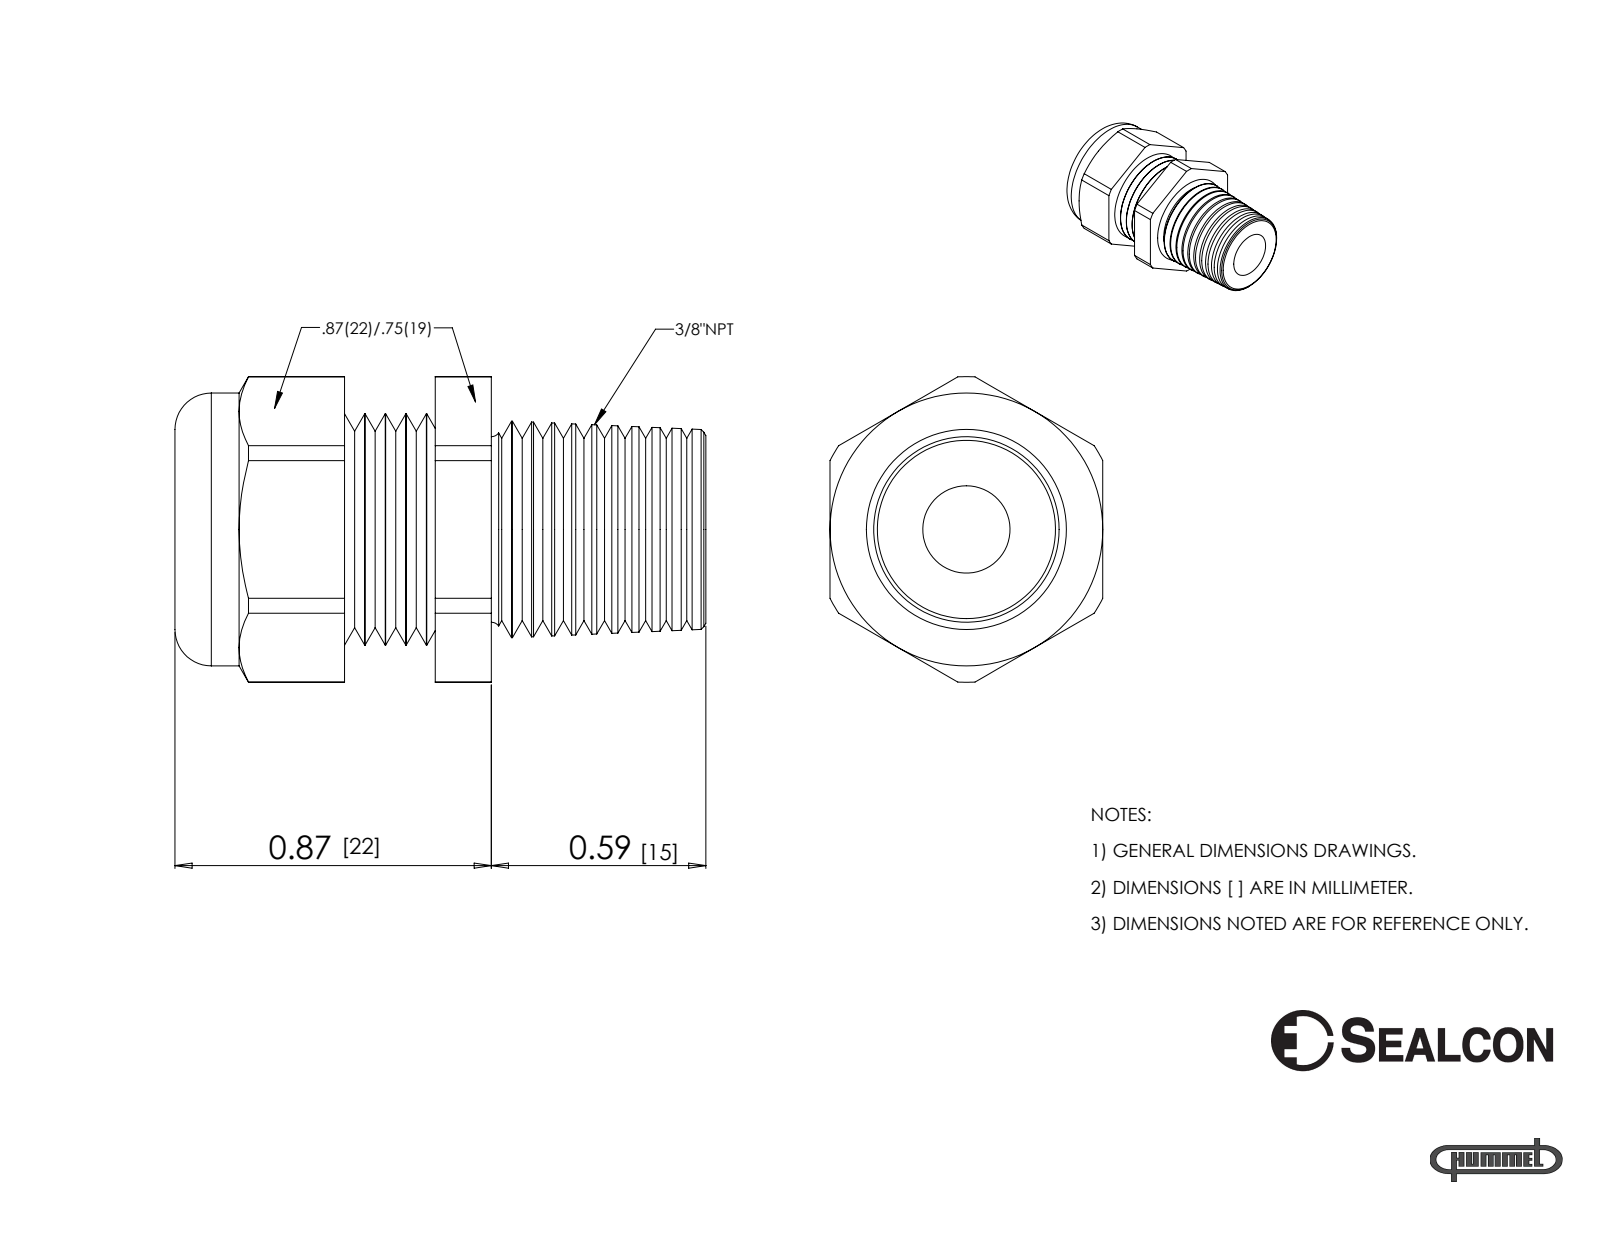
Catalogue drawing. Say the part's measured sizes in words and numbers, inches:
The part is named "CD09NR-GY". Its 3-D file was written by "SolidWorks 2009 (CONFIG_CONTROL_DESIGN)". It is 2 solids with 152 faces: 20 planar, 32 cylindrical and 100 other. Overall it measures 1.46 by 0.84 by 0.75 inches. Its volume is 0.407 cubic inches and its surface area 7.52 square inches. Round holes: 1 of diameter 0.24, 1 of diameter 0.51. Round bosses or shafts: 1 of diameter 0.75, 1 of diameter 0.636. Partial cylindrical surfaces (rounded edges, fillets, slot ends): 1 of radius 0.42. The main face-to-face distances are 0.75, 0.694, 0.539, 0.154, 0.29, 0.25, 0.404, 0.75, 0.156, 0.446.
